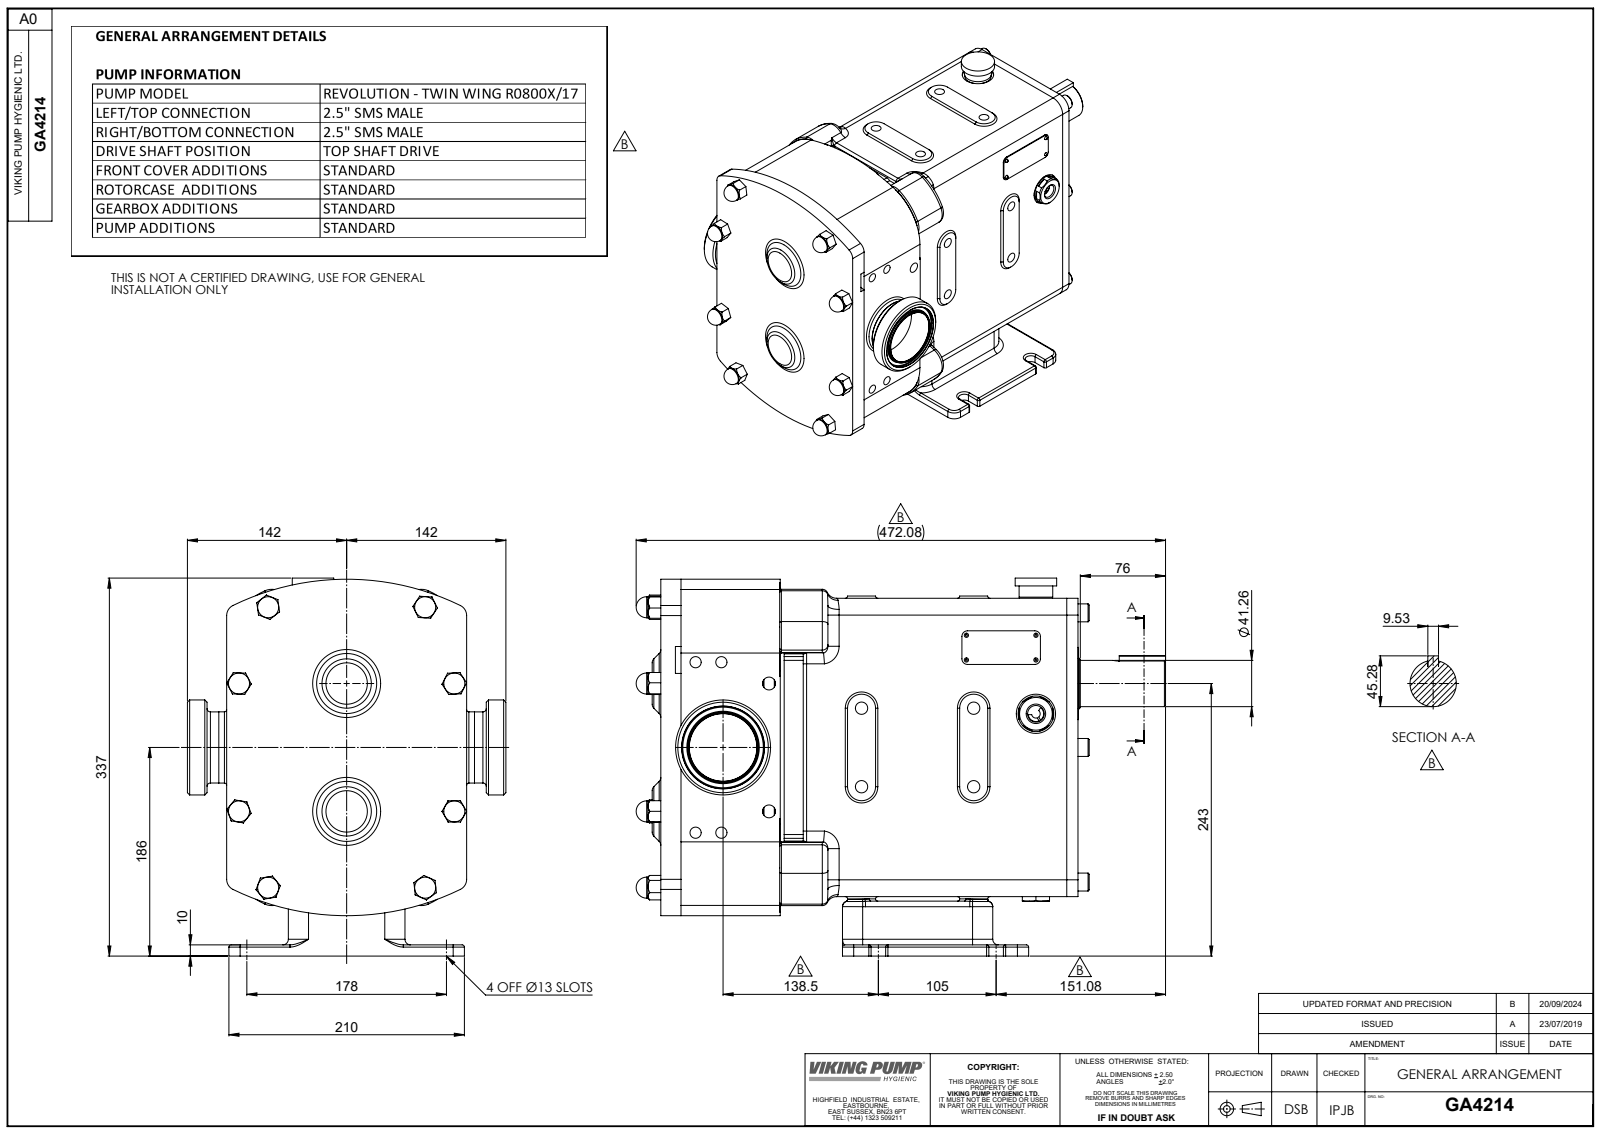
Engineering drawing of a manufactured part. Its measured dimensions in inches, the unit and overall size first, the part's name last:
Units: inches
Overall size (bounding box): 18.585 × 13.268 × 11.181
Round holes (diameter × count): ⌀0.433 ×8, ⌀0.394 ×4, ⌀1.378 ×4, ⌀0.453 ×2, ⌀0.585 ×1, ⌀2.374 ×1, ⌀2.894 ×1
Round bosses / shafts (diameter × count): ⌀0.63 ×10, ⌀0.74 ×8, ⌀3.335 ×1, ⌀2.5 ×1, ⌀2.496 ×1, ⌀2.48 ×1, ⌀1.772 ×1, ⌀1.624 ×1
Partial cylindrical surfaces — rounded edges, fillets, slot ends (radius × count): R0.079 ×38, R0.394 ×34, R0.197 ×27, R0.232 ×8, R0.591 ×8, R0.709 ×8, R0.118 ×4, R0.256 ×4
Main face-to-face distances: 5.984, 14.646, 1.22, 7.205, 1.693, 10.472, 12.008, 2.638, 0.394, 1.929
Hole centre spacings: 2.194, 2.756, 3.365, 3.937, 4.806, 6.125, 6.635, 0.906
Volume: 1 061 in³ · Surface area: 1 193 in²
Bodies: 3 solids, 1323 faces (475 planar, 424 cylindrical, 424 other)
Part name (STEP PRODUCT): Copy of Z94-5101-44 - 2.5 INCH SMS681^GA4214; GA4214; Copy of R0800 CPP H TSD^GA4214
STEP written by: SolidWorks 2023 (AUTOMOTIVE_DESIGN)
